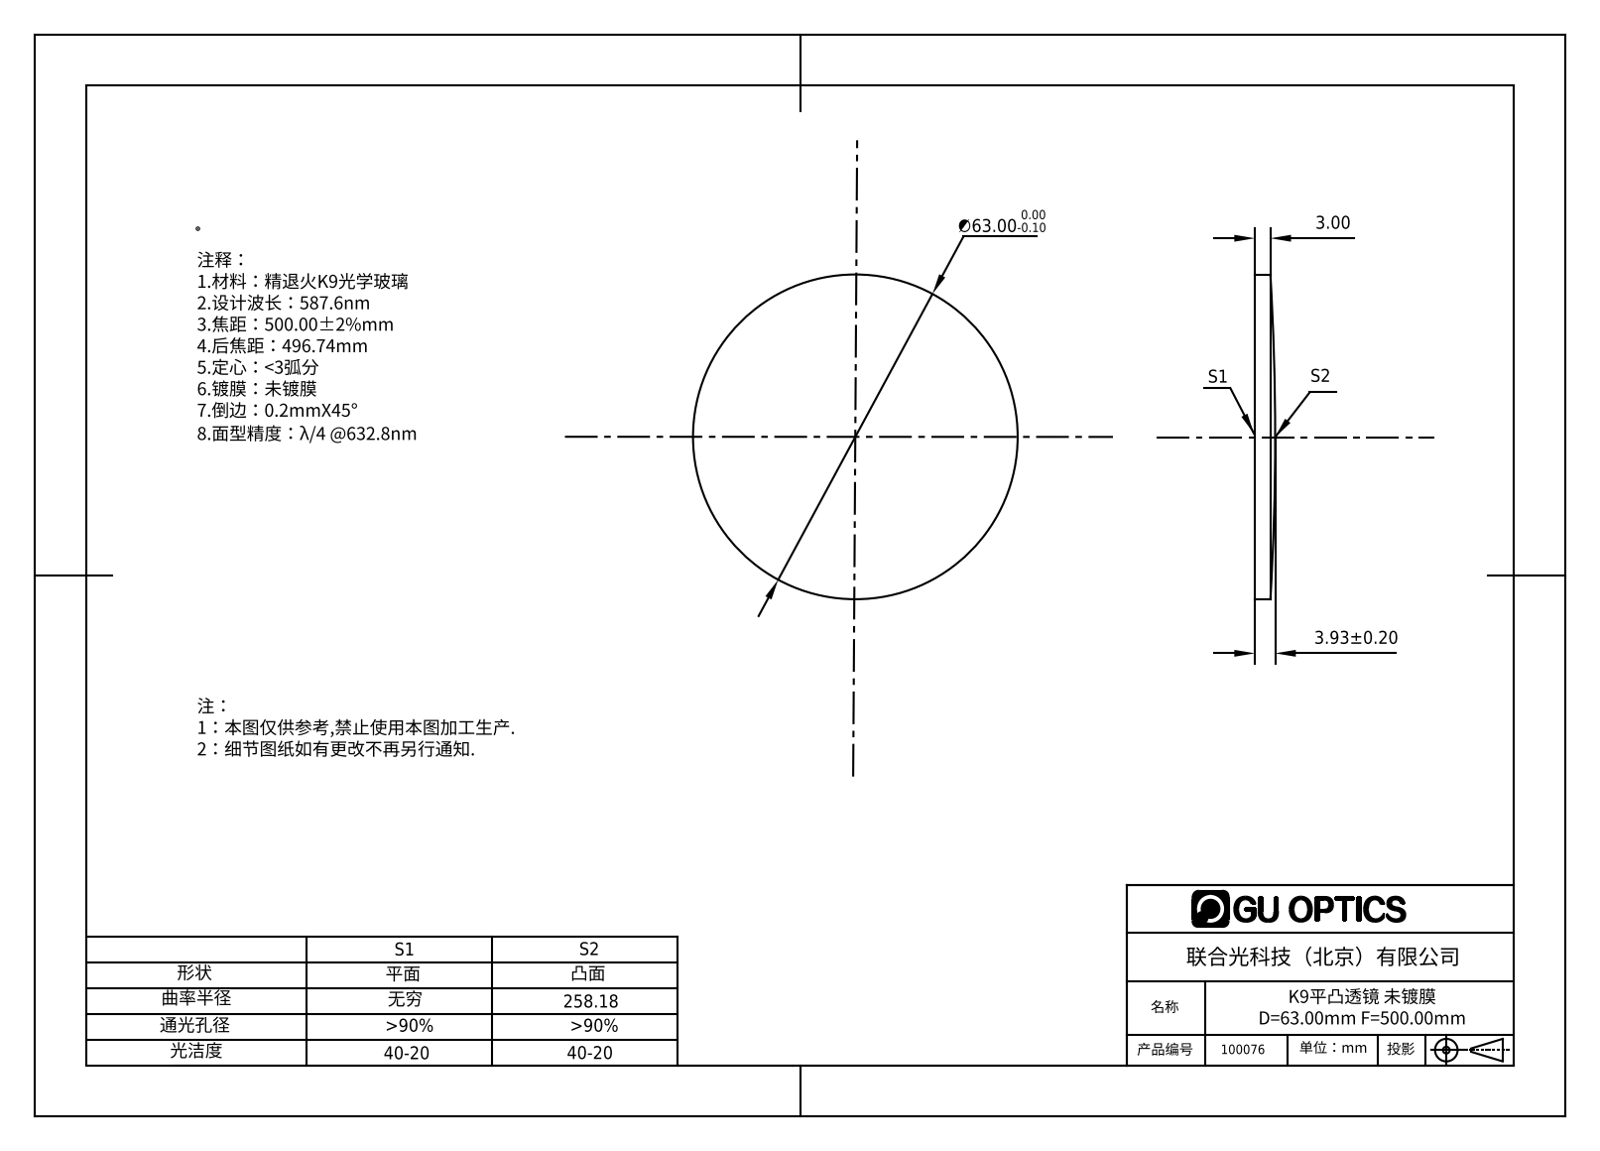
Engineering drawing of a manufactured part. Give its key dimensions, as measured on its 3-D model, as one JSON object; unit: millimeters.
{"part_name": "100076", "step_written_by": "SolidWorks 2016 (AUTOMOTIVE_DESIGN)", "units": "millimeters", "bodies": {"solids": 1, "faces": 5, "planar": 1, "cylindrical": 2, "other": 2}, "overall_size": [63, 63, 3.93], "volume_mm3": 10802, "surface_area_mm2": 6831, "round_bosses_or_shafts": [[63, 1]]}
